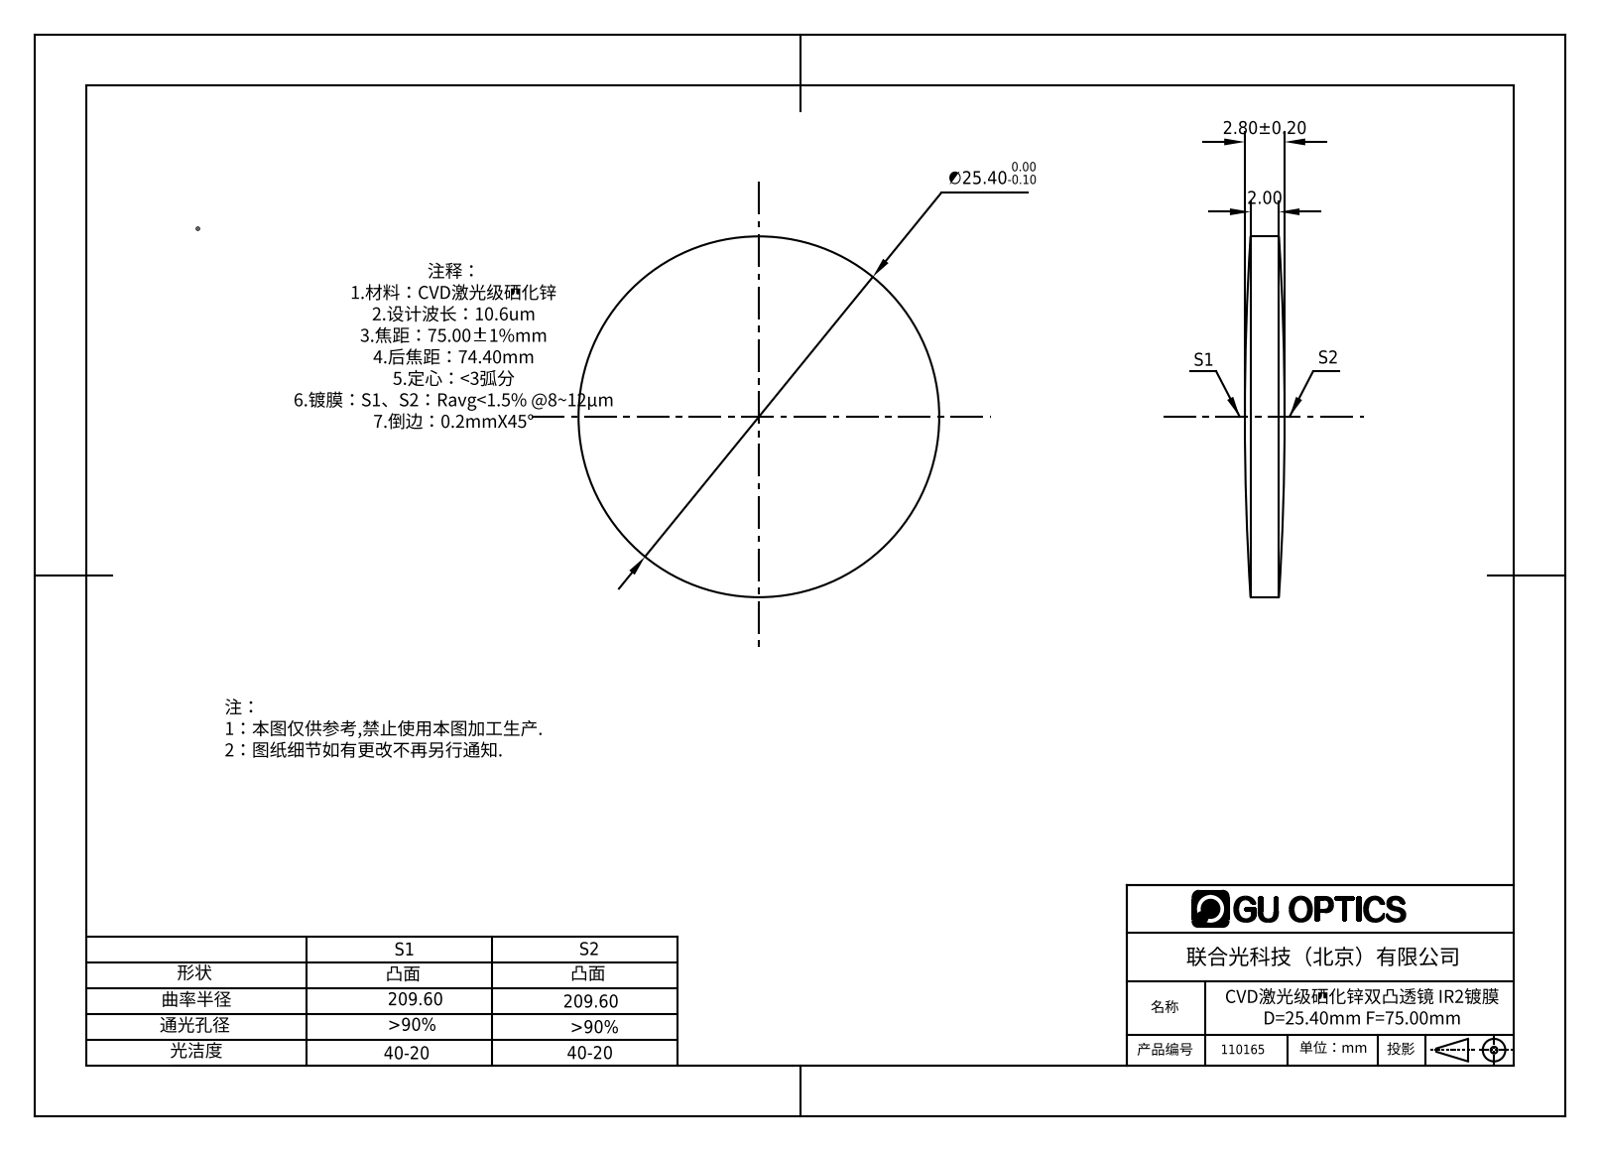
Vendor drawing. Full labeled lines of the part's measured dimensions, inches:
Part name (STEP PRODUCT): 110157
STEP written by: SolidWorks 2016 (CONFIG_CONTROL_DESIGN)
Units: inches
Bodies: 1 solid, 6 faces (0 planar, 2 cylindrical, 4 other)
Overall size (bounding box): 1 × 1 × 0.11
Volume: 0.074 in³ · Surface area: 1.82 in²
Round bosses / shafts (diameter × count): ⌀1 ×1
